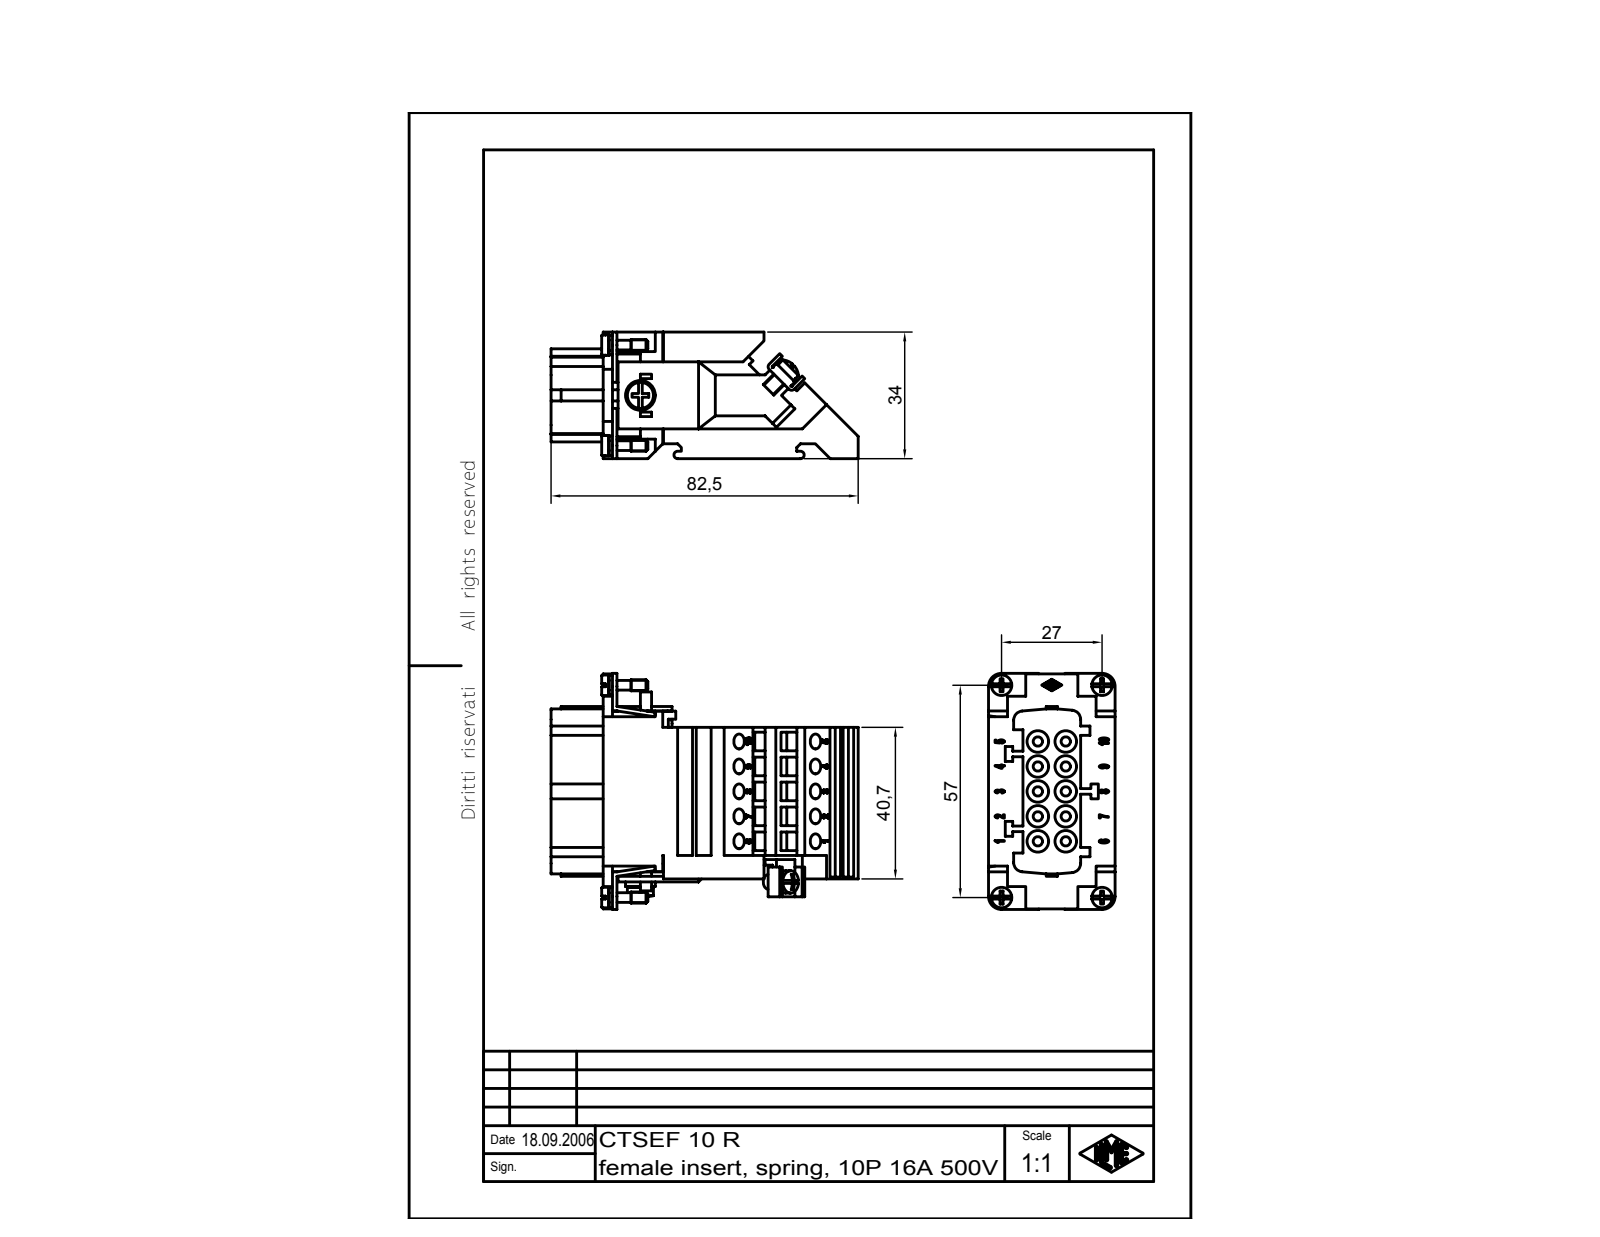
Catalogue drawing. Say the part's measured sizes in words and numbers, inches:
The part is named "CTSEF 10 R". Its 3-D file was written by "Autodesk Inventor 7 (AUTOMOTIVE_DESIGN)". It is 1 solid with 1035 faces: 554 planar, 78 cylindrical and 403 other. Overall it measures 3.248 by 2.496 by 1.339 inches. Its volume is 4.892 cubic inches and its surface area 39.05 square inches. Round holes: 10 of diameter 0.157, 1 of diameter 0.128. Round bosses or shafts: 2 of diameter 0.217, 2 of diameter 0.209, 2 of diameter 0.118, 2 of diameter 0.102, 1 of diameter 0.315, 1 of diameter 0.276, 1 of diameter 0.236, 1 of diameter 0.157. Partial cylindrical surfaces (rounded edges, fillets, slot ends): 14 of radius 0.004, 6 of radius 0.039, 4 of radius 0.098, 2 of radius 0.008, 2 of radius 0.138. The main face-to-face distances are 0.157, 0.059, 1.339, 0.079, 0.049, 0.974, 0.364, 0.177, 0.248, 0.315. The hole center spacings are 0.264, 0.957, 0.528, 1.061, 0.92, 0.791, 1.213, 1.055.
